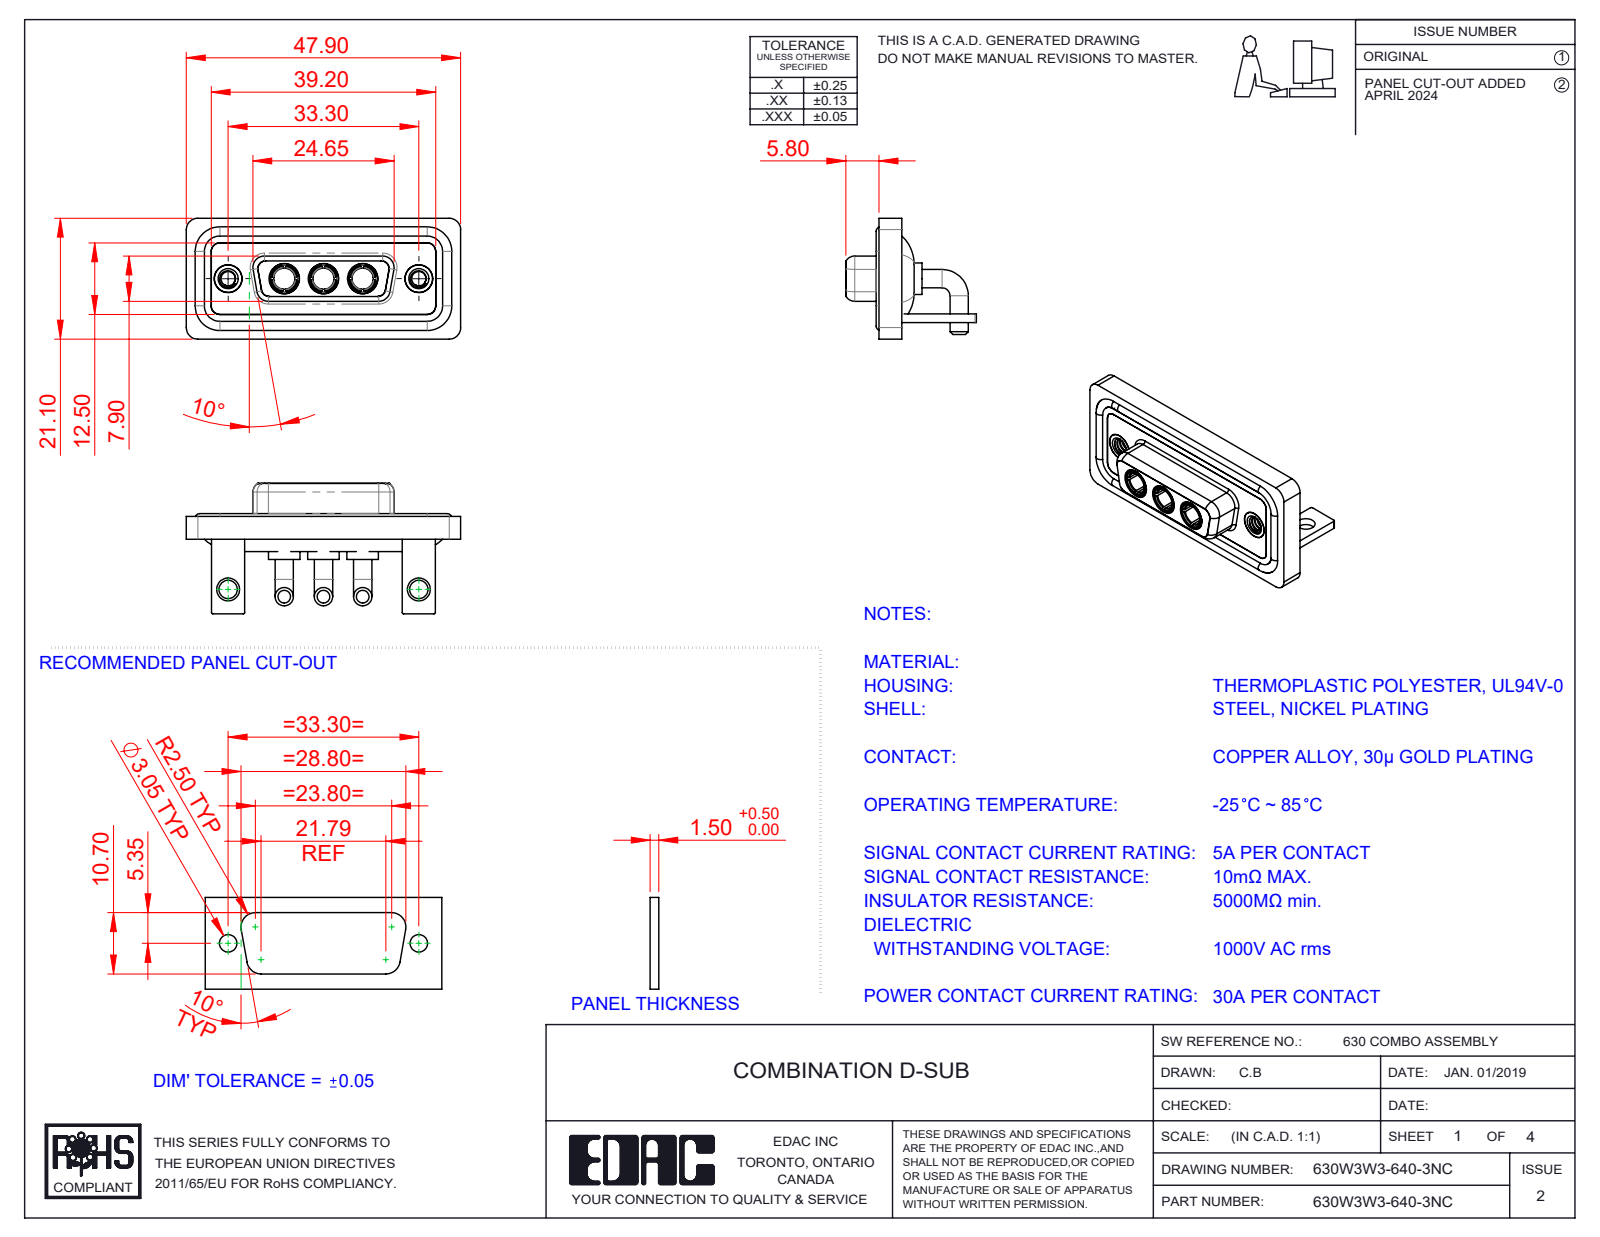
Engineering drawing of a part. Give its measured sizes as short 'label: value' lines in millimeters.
name: 630Combo Threaded Rivet_A; 630Combo Shell Rear_15 Contacts; 630W3W3-640-3NC; 630Combo Shell Front_15 Contacts (+4 more)
written by: SolidWorks 2023 (CONFIG_CONTROL_DESIGN)
unit: mm
bodies: 15 solids, 662 faces (212 planar, 285 cylindrical, 165 other)
size: 47.9 × 22.8 × 21.1
volume: 6 623 mm³; area: 10 766 mm²
holes: 5× ⌀4.85, 3× ⌀3.7, 3× ⌀5.3, 2× ⌀2.5, 2× ⌀3.2, 2× ⌀4, 2× ⌀4.05, 2× ⌀5
bosses: 6× ⌀3.2, 4× ⌀1.6, 3× ⌀5.5, 3× ⌀5.2, 3× ⌀4.96, 3× ⌀4.75, 3× ⌀3.75, 2× ⌀4.95
rounds: 21× R2, 18× R1.5, 16× R0.25, 12× R1.35, 8× R1.6, 5× R0.5, 4× R0.6, 4× R0.65
face distances: 0.4, 2.9, 1.5, 1.8, 3.7, 1.1, 4.1, 1.6, 2.5, 1.4
hole spacings: 6.85, 9.8, 16.65, 23.5, 33.3, 13.7
